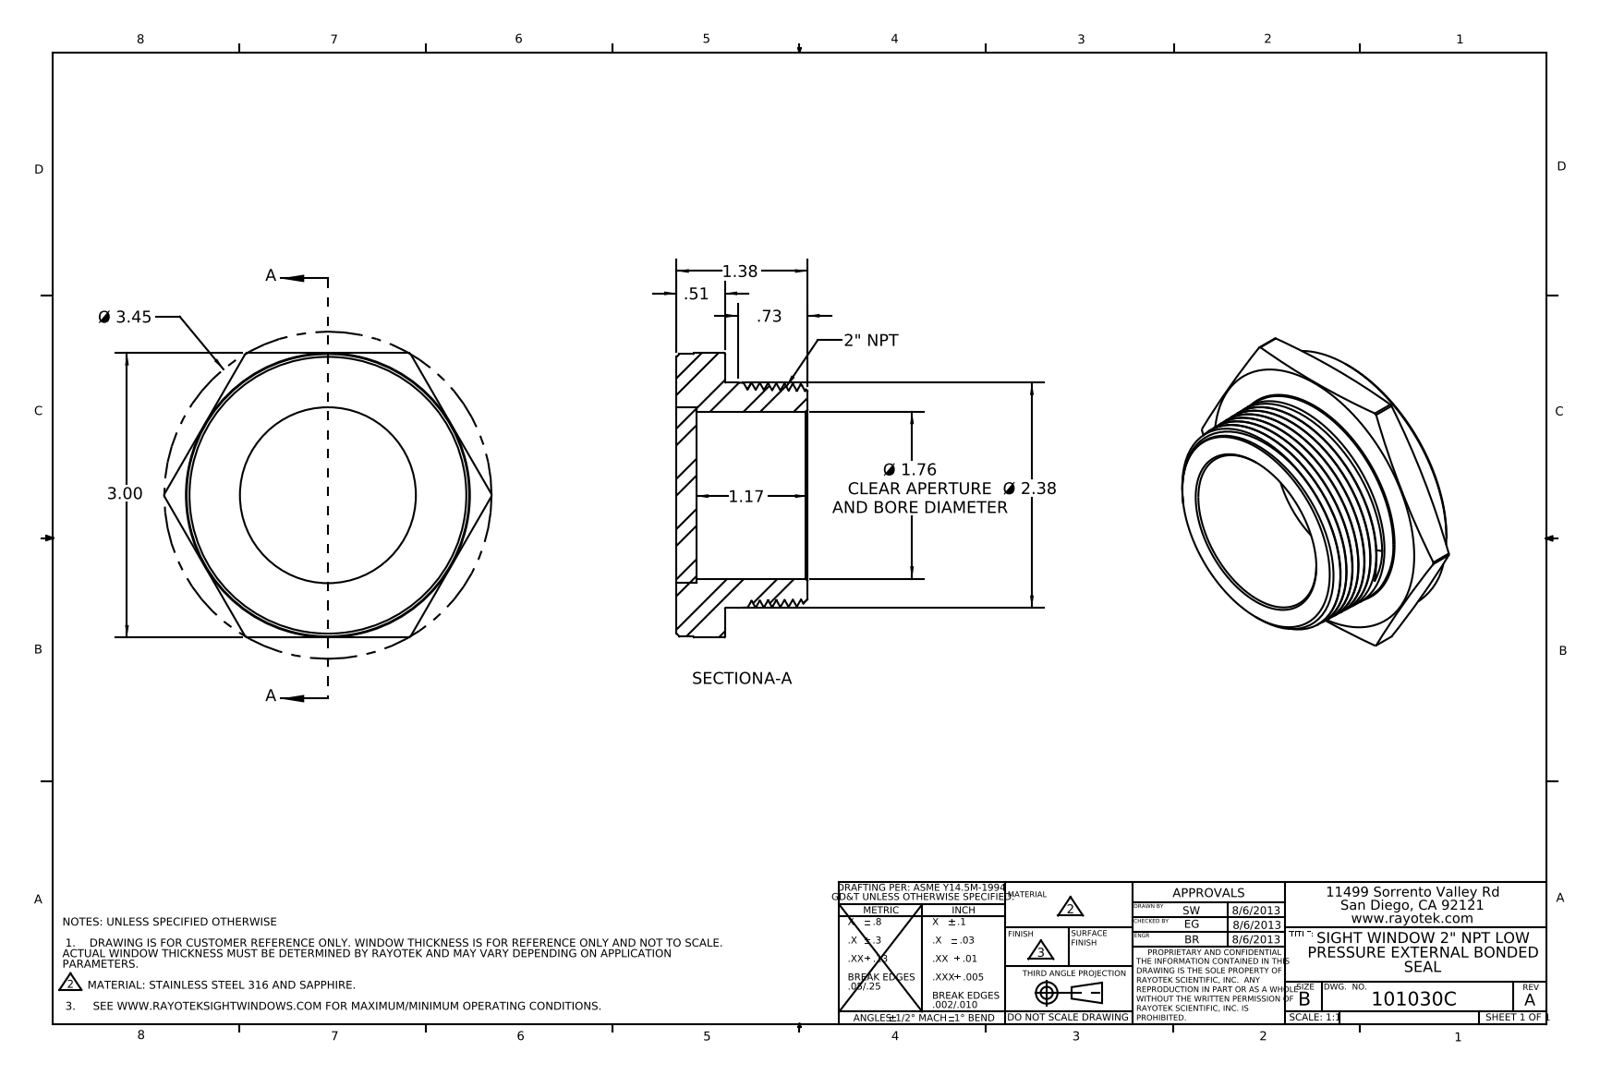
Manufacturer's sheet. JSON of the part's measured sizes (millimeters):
{"part_name": "403030", "step_written_by": "SolidWorks 2012 (AUTOMOTIVE_DESIGN)", "units": "millimeters", "bodies": {"solids": 2, "faces": 65, "planar": 15, "cylindrical": 17, "other": 33}, "overall_size": [87.7, 76.2, 35.1], "volume_mm3": 75090, "surface_area_mm2": 25360, "round_holes": [[44.7, 1], [47.1, 1]], "round_bosses_or_shafts": [[75.7, 1], [60.3, 1]], "partial_cylinders_radius": [[43.8, 1]], "face_to_face_distances": [5.3, 13, 7.7, 76.2, 35.1, 29.8, 22.1]}
